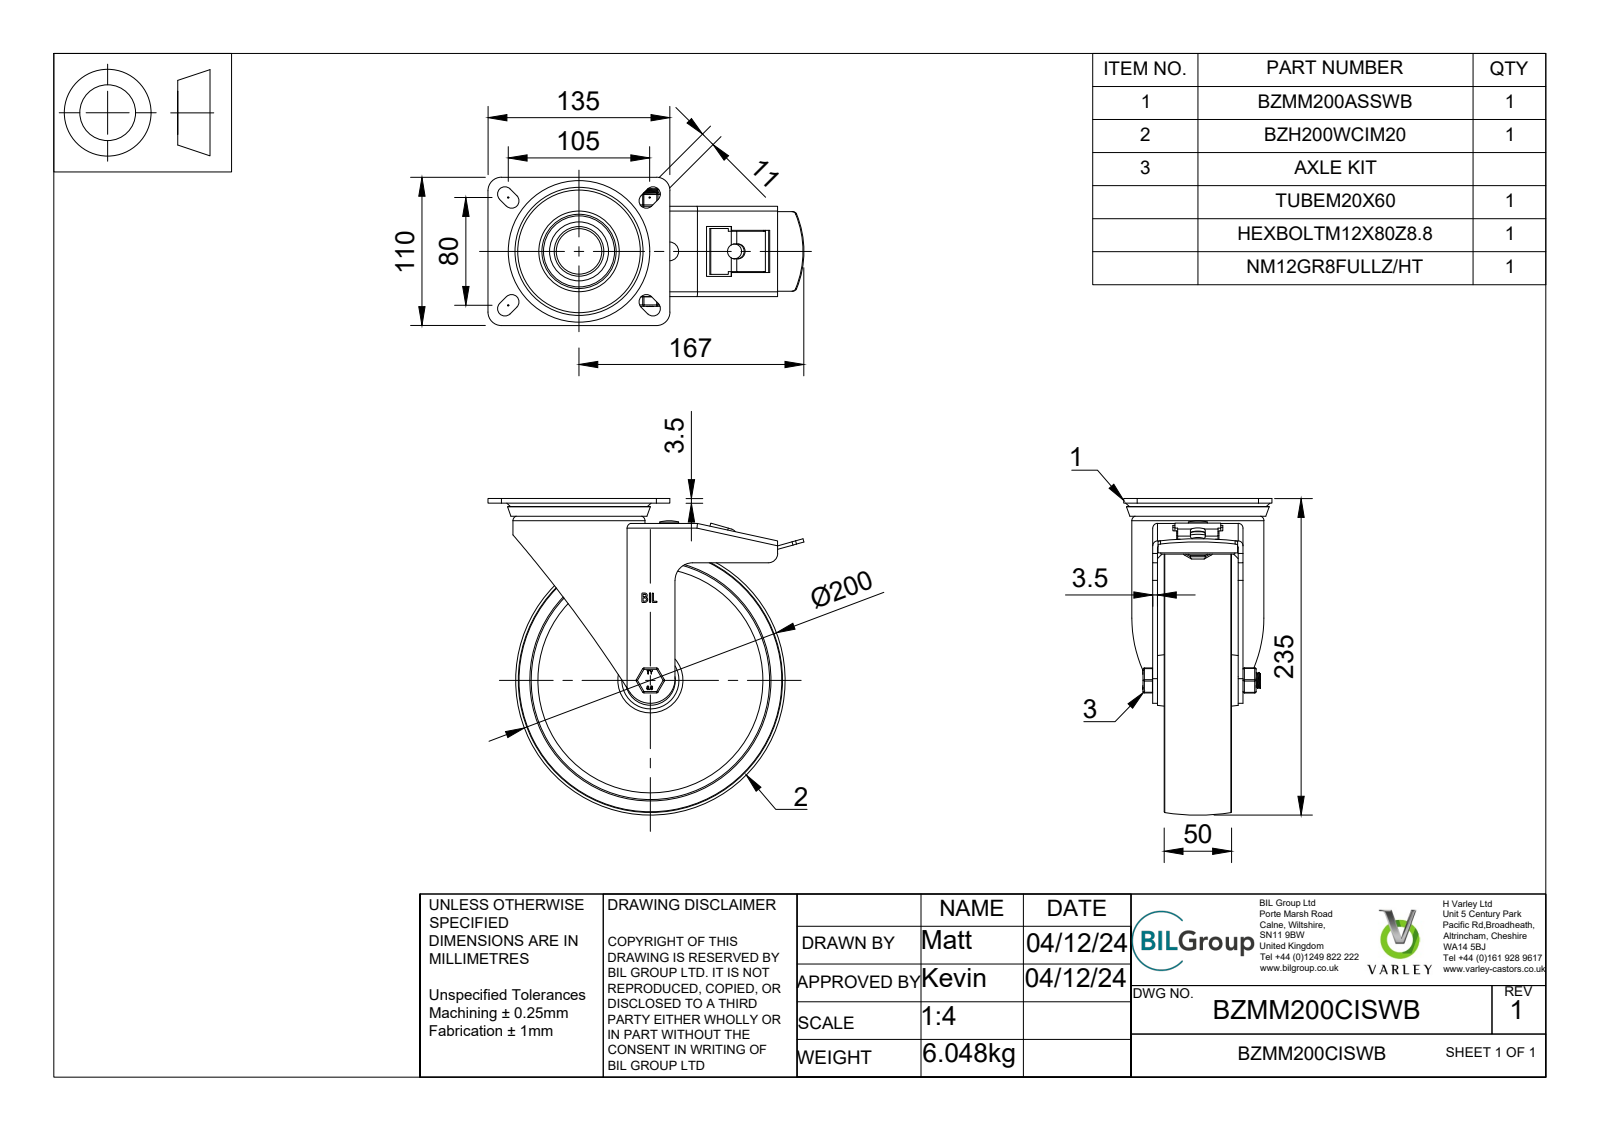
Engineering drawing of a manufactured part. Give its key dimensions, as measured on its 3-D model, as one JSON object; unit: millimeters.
{"part_name": "BZMM200CISWB v3; BZMM200ASSWB v1; ZINC PLATED, PRESSED STEEL TOP PLATE; ZINC PLATED, PRESSED STEEL TOP PLATE Geometry (+7 more)", "step_written_by": "Autodesk Translation Framework v13.20.0.188 (AP242_MANAGED_MODEL_BASED_3D_ENGINEERING_MIM_LF)", "units": "millimeters", "bodies": {"solids": 53, "faces": 550, "planar": 246, "cylindrical": 153, "other": 151}, "overall_size": [235, 234.5, 110], "volume_mm3": 865046, "surface_area_mm2": 278961, "round_holes": [[8, 1], [11, 1], [12, 1], [12.2, 1], [12.5, 1], [20.2, 1], [33.75, 1], [61, 1], [91, 1], [177, 1]], "round_bosses_or_shafts": [[98, 1], [78, 1], [50, 1], [39.75, 1], [19.9, 1], [18, 1], [14, 1], [11.83, 1]], "partial_cylinders_radius": [[1, 32], [5.5, 10], [1.75, 7], [0.25, 6], [2.5, 6], [3.5, 4], [10, 4], [3, 2]], "face_to_face_distances": [3.5, 10, 25, 5, 35, 28.5, 38.5, 63.5, 13, 9], "hole_center_spacings": [67]}
